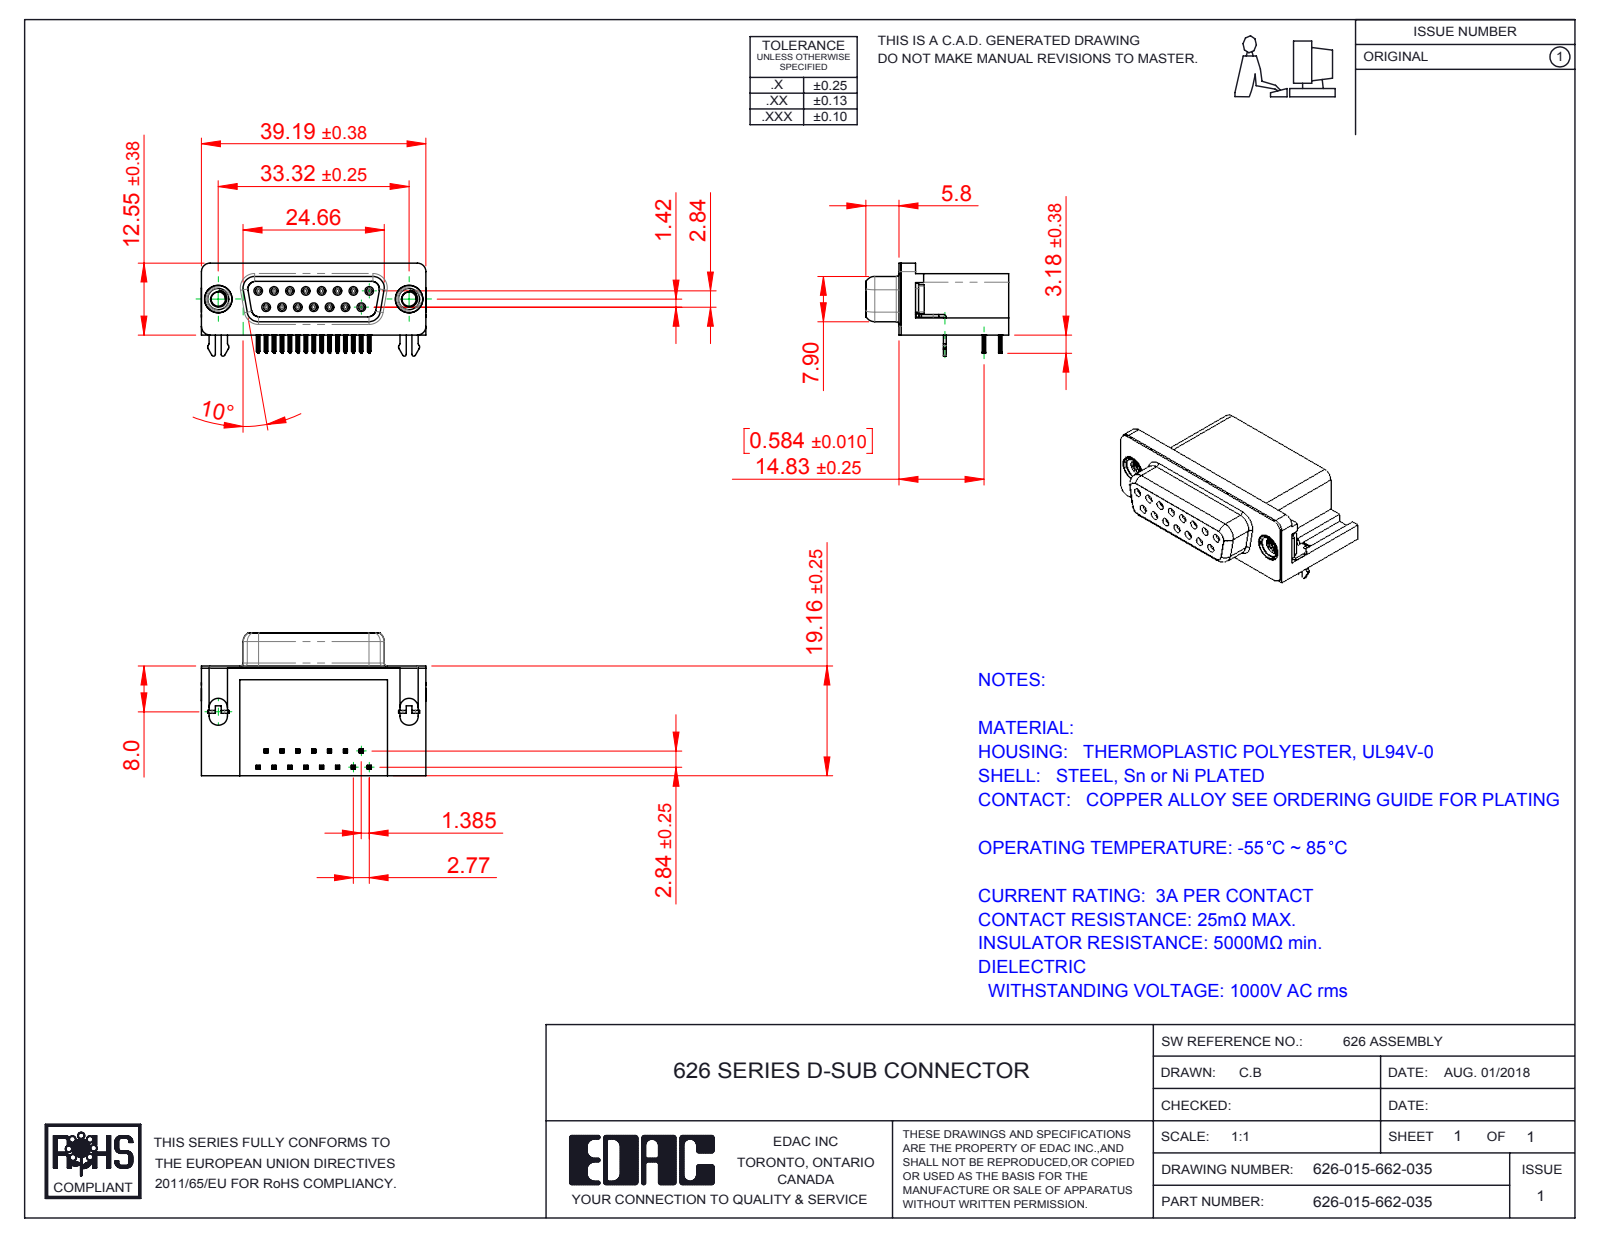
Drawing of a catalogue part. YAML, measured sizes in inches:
part_name: "626 Contact Bottom; 626 2 Prong Board Lock; 626 Contact Top; 626-015-662-035 (+3 more)"
step_written_by: "SolidWorks 2016 (CONFIG_CONTROL_DESIGN)"
units: inches
bodies: {solids: 21, faces: 2465, planar: 1104, cylindrical: 617, other: 744}
overall_size: [1.544, 0.983, 0.64]
volume: 0.442
surface_area: 12.46
round_holes:
  - {diameter: 0.031, count: 15}
  - {diameter: 0.035, count: 15}
  - {diameter: 0.098, count: 2}
  - {diameter: 0.157, count: 2}
  - {diameter: 0.189, count: 2}
  - {diameter: 0.197, count: 2}
round_bosses_or_shafts:
  - {diameter: 0.047, count: 15}
  - {diameter: 0.193, count: 2}
  - {diameter: 0.187, count: 2}
  - {diameter: 0.154, count: 2}
partial_cylinders:
  - {radius: 0.004, count: 120}
  - {radius: 0.006, count: 60}
  - {radius: 0.014, count: 30}
  - {radius: 0.039, count: 18}
  - {radius: 0.013, count: 15}
  - {radius: 0.02, count: 10}
  - {radius: 0.01, count: 8}
  - {radius: 0.053, count: 8}
face_to_face_distances: [0.016, 0.407, 0.739, 0.014, 0.244, 0.107, 0.754, 0.421, 0.369, 0.125]
hole_center_spacings: [0.124, 0.109, 0.218, 0.327, 0.436, 0.198, 0.198, 0.294]
